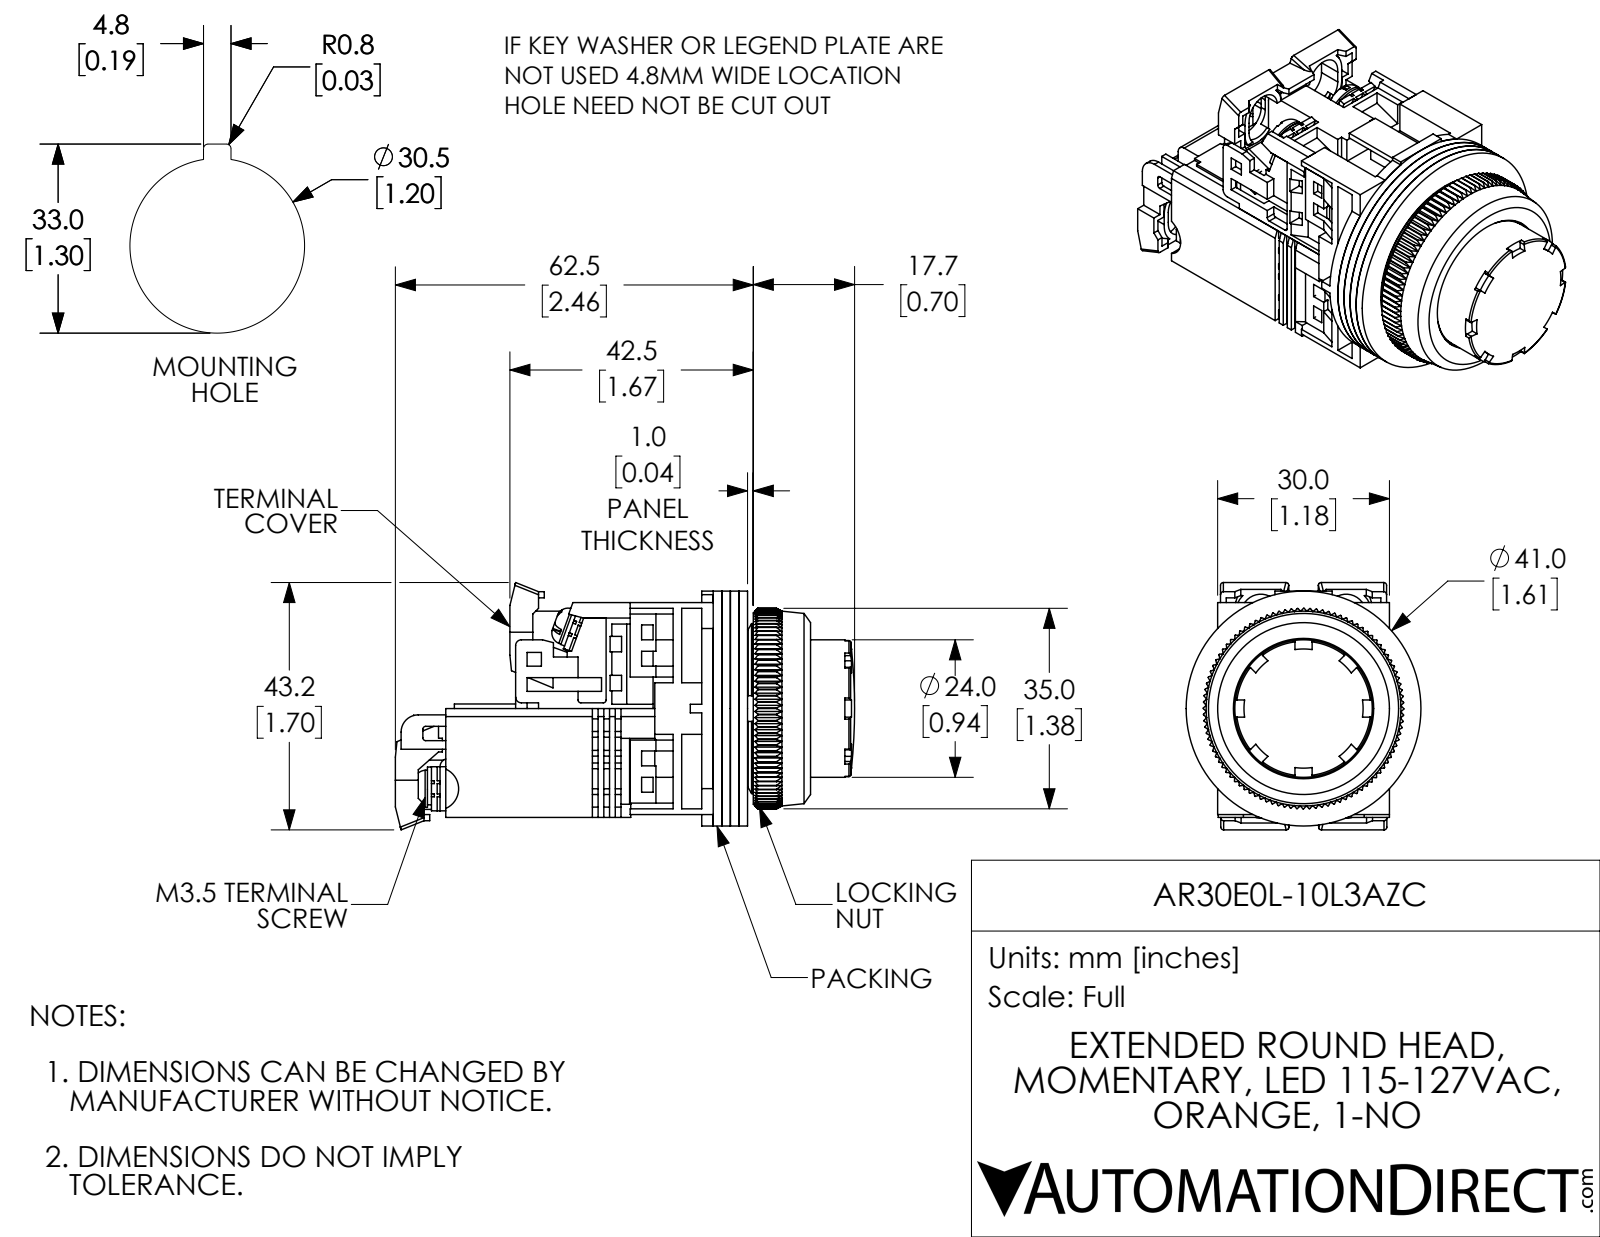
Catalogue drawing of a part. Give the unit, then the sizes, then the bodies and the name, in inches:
Units: inches
Overall size (bounding box): 3.157 × 1.7 × 1.614
Round holes (diameter × count): ⌀0.138 ×6, ⌀0.142 ×4, ⌀0.118 ×3, ⌀0.472 ×1, ⌀0.709 ×1, ⌀0.728 ×1, ⌀0.787 ×1, ⌀0.945 ×1, ⌀0.965 ×1, ⌀1.122 ×1, ⌀1.252 ×1
Round bosses / shafts (diameter × count): ⌀0.26 ×4, ⌀0.138 ×2, ⌀1.614 ×1, ⌀1.181 ×1, ⌀0.866 ×1, ⌀0.776 ×1, ⌀0.551 ×1
Partial cylindrical surfaces — rounded edges, fillets, slot ends (radius × count): R0.059 ×17, R0.012 ×16, R0.02 ×13, R0.138 ×4, R0.177 ×4, R0.039 ×2, R0.118 ×2, R0.016 ×1
Main face-to-face distances: 0.059, 0.118, 0.177, 0.748, 0.039, 0.02, 0.079, 1.417, 0.689, 0.047
Hole centre spacings: 0.579, 0.02, 0.295, 0.299, 0.3, 0.583, 0.583, 0.605
Volume: 2.883 in³ · Surface area: 64.03 in²
Bodies: 27 solids, 1960 faces (1368 planar, 339 cylindrical, 253 other)
Part name (STEP PRODUCT): AR30E0L-10L3AZC
STEP written by: SolidWorks 2017 (AUTOMOTIVE_DESIGN)
